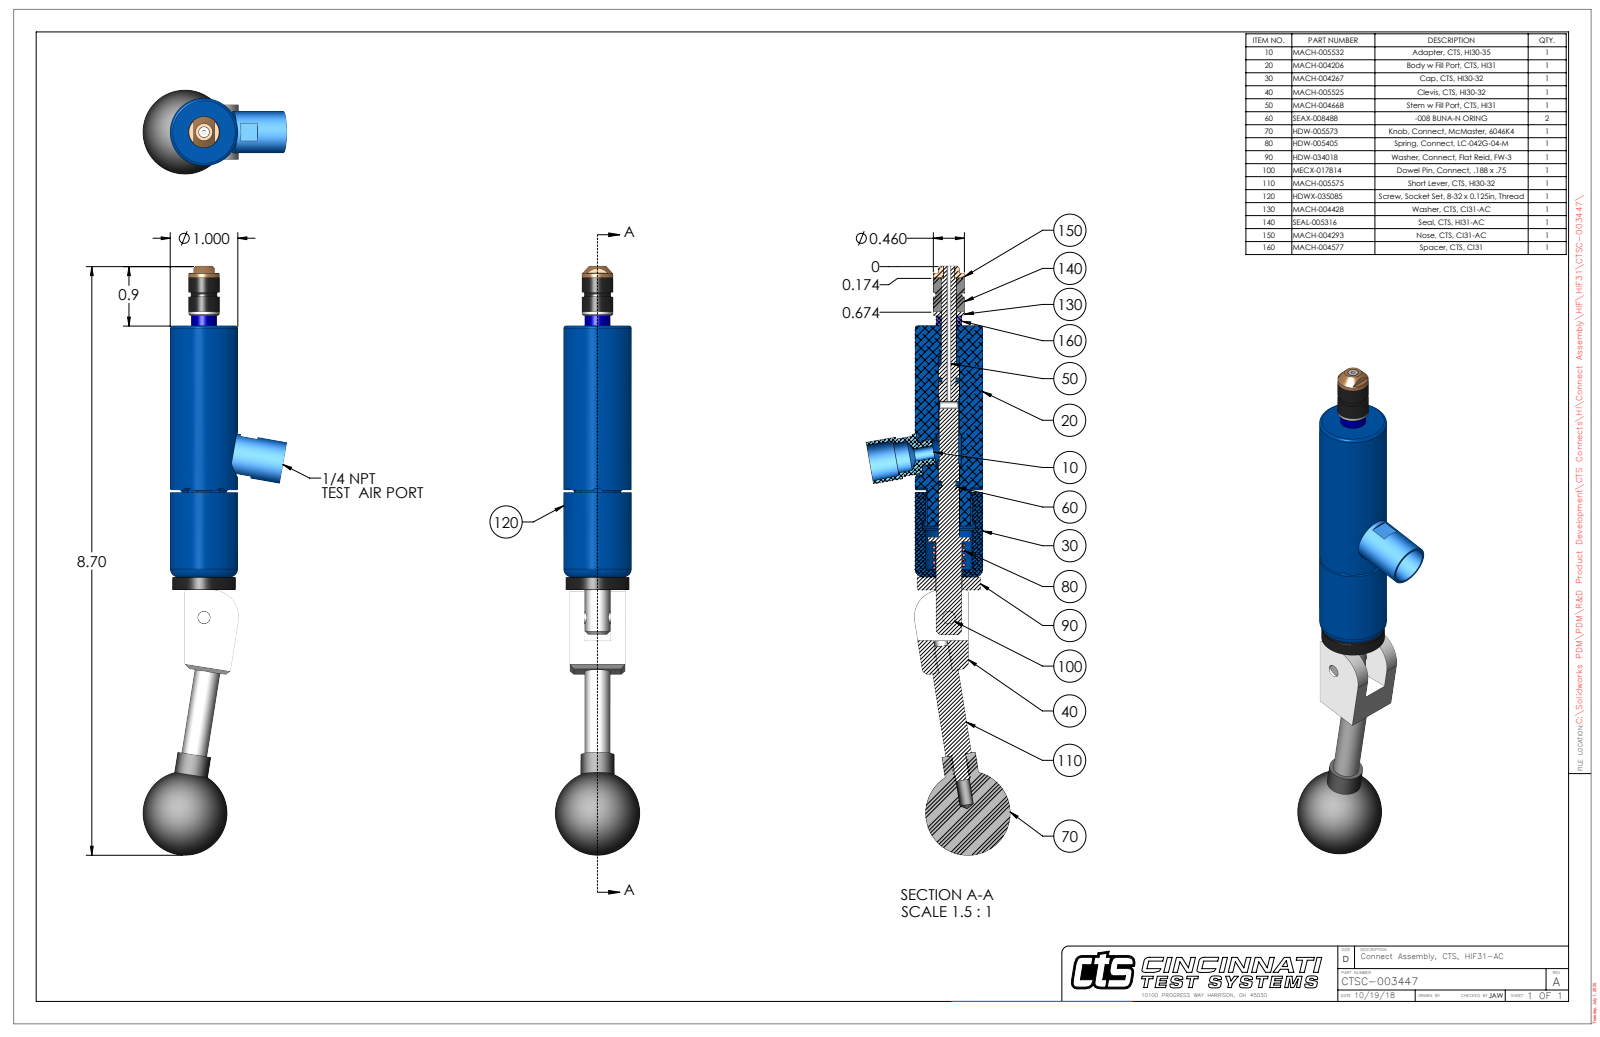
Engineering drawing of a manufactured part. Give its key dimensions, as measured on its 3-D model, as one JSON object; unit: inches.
{"part_name": "CTSC-003447", "step_written_by": "SolidWorks 2023 (AUTOMOTIVE_DESIGN)", "units": "inches", "bodies": {"solids": 10, "faces": 283, "planar": 98, "cylindrical": 121, "other": 64}, "overall_size": [8.704, 2.128, 1.25], "volume_in3": 4.991, "surface_area_in2": 38.22, "round_holes": [[0.201, 2], [0.063, 1], [0.105, 1], [0.109, 1], [0.136, 1], [0.15, 1], [0.159, 1], [0.187, 1], [0.189, 1], [0.218, 1], [0.228, 1], [0.229, 1]], "round_bosses_or_shafts": [[1, 1], [0.936, 1], [0.62, 1], [0.5, 1], [0.462, 1], [0.46, 1], [0.38, 1], [0.379, 1]], "partial_cylinders_radius": [[0.093, 6], [0.029, 2], [0.325, 1], [0.4, 1], [0.474, 1]], "face_to_face_distances": [0.21, 0.602, 0.812, 0.187, 3.716, 3.903, 0.391, 2.463, 1.253, 1.441], "hole_center_spacings": [0.599, 1.658, 2.252]}
